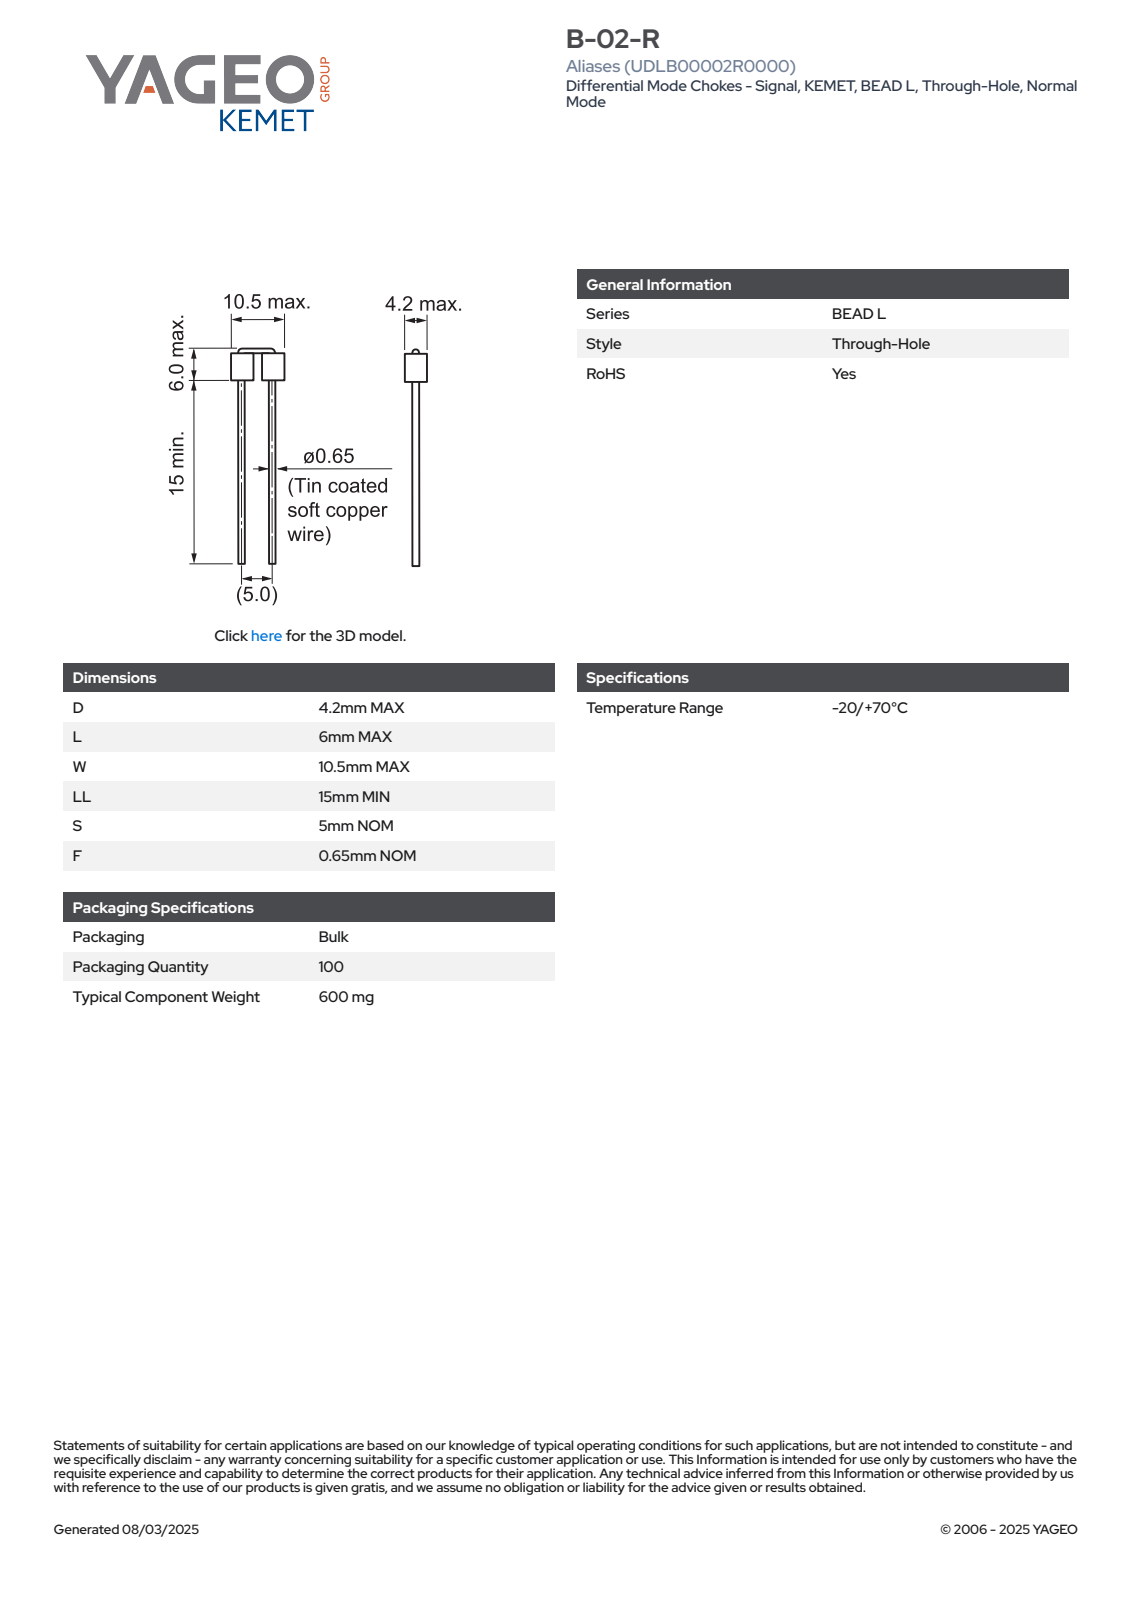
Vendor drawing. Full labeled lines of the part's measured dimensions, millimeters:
Part name (STEP PRODUCT): IL_B02R_D3.6L7.5L24.60S5LL20LL210
STEP written by: SolidWorks 2014 (AUTOMOTIVE_DESIGN)
Units: millimetres
Bodies: 2 solids, 145 faces (51 planar, 28 cylindrical, 66 other)
Overall size (bounding box): 21 × 10.5 × 4.21
Volume: 160 mm³ · Surface area: 269 mm²
Round bosses / shafts (diameter × count): ⌀0.65 ×3, ⌀4.2 ×2
Partial cylindrical surfaces — rounded edges, fillets, slot ends (radius × count): R2.11 ×2
Main face-to-face distances: 5.35, 15, 20.35
